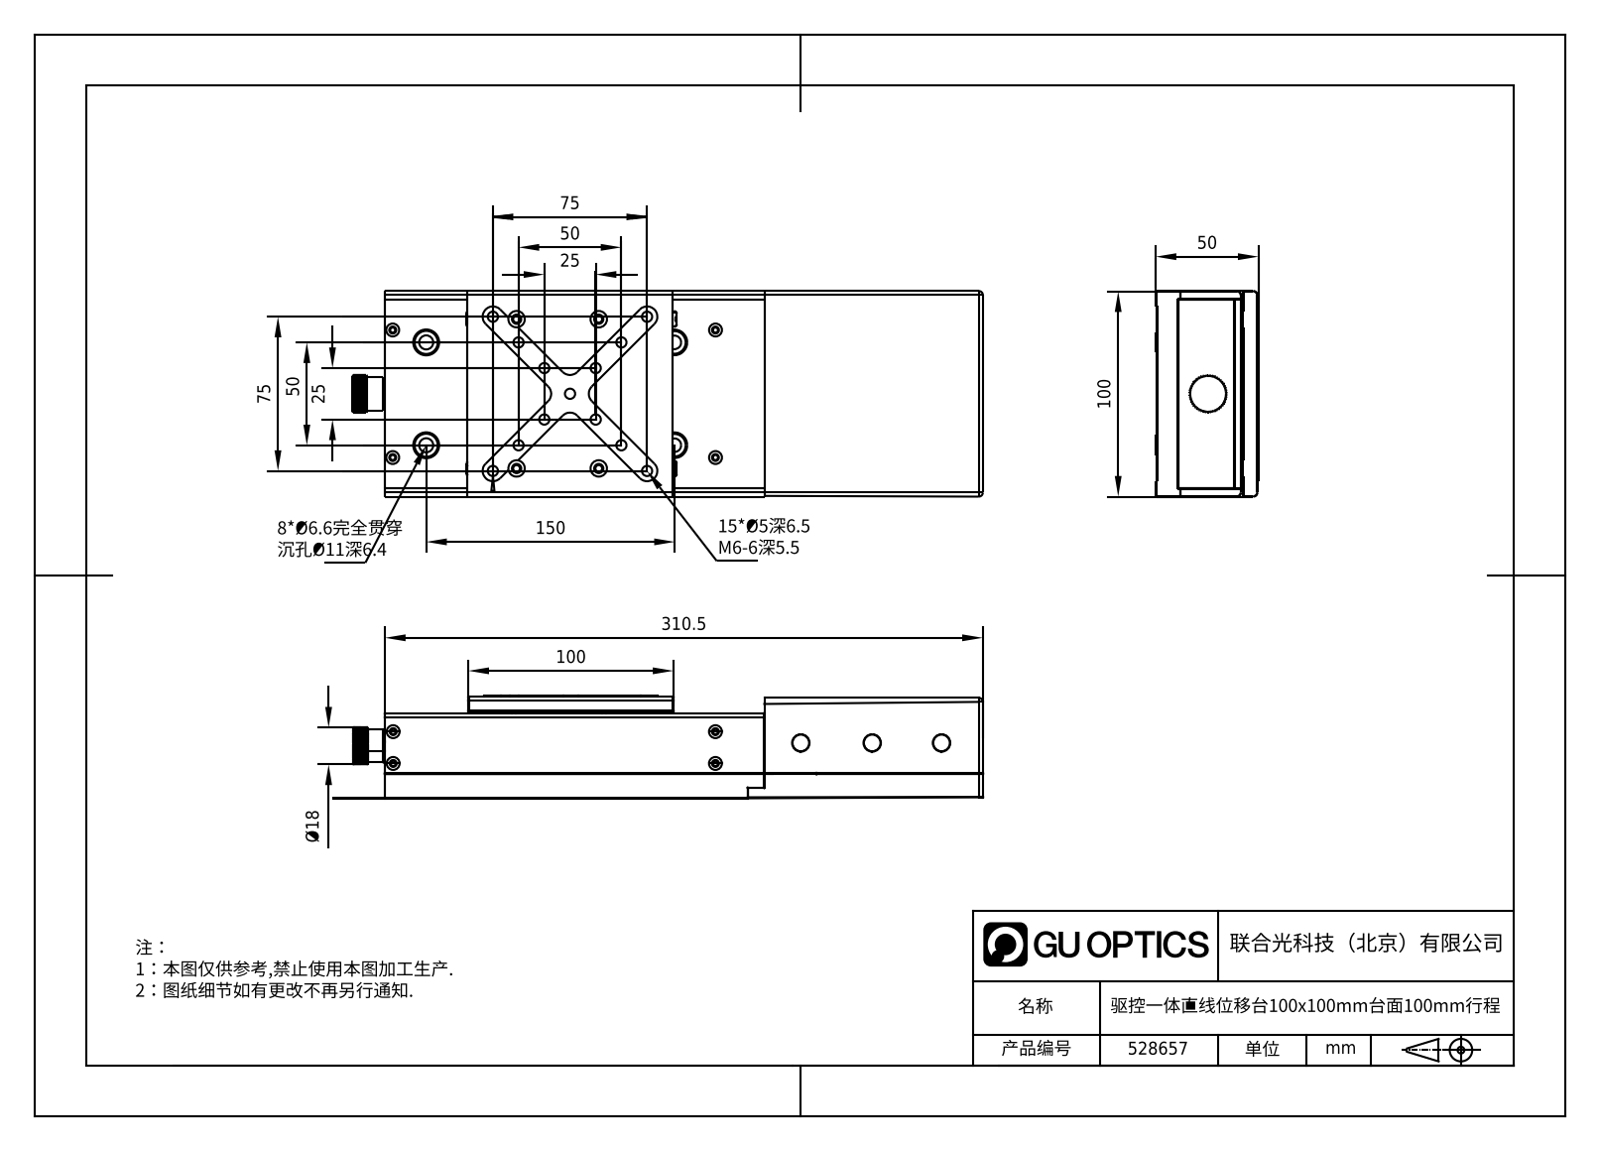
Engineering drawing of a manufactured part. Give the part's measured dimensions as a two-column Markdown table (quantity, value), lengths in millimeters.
| quantity | value |
| --- | --- |
| part name | 528657 |
| STEP written by | SolidWorks 2020 (CONFIG_CONTROL_DESIGN) |
| units | millimeters |
| bodies | 47 solids, 2432 faces (1207 planar, 856 cylindrical, 369 other) |
| overall size | 310.5 × 100 × 48 |
| volume | 811 950 mm³ |
| surface area | 298 137 mm² |
| round holes (diameter × count) | 2.4 × 40, 4.2 × 26, 1.6 × 24, 3.4 × 21, 2.5 × 20, 1.57 × 16, 4.4 × 16, 5 × 14, 6.5 × 9, 6.6 × 8, 11 × 8, 12.5 × 8 |
| round bosses / shafts (diameter × count) | 2.2 × 4, 14 × 2, 3.8 × 2, 2 × 2, 22 × 1, 16 × 1, 13 × 1, 3 × 1 |
| partial cylindrical surfaces (radius × count) | 2 × 29, 1 × 17, 5 × 12, 0.75 × 7, 0.7 × 4, 1.35 × 4, 0.3 × 2, 0.4 × 2 |
| main face-to-face distances | 4, 1, 26.5, 7, 8, 30.5, 0.5, 3, 9.5, 39 |
| hole center spacings | 17.68, 35.36, 10.5, 55.9, 39.53, 53.03, 63.74, 5 |
